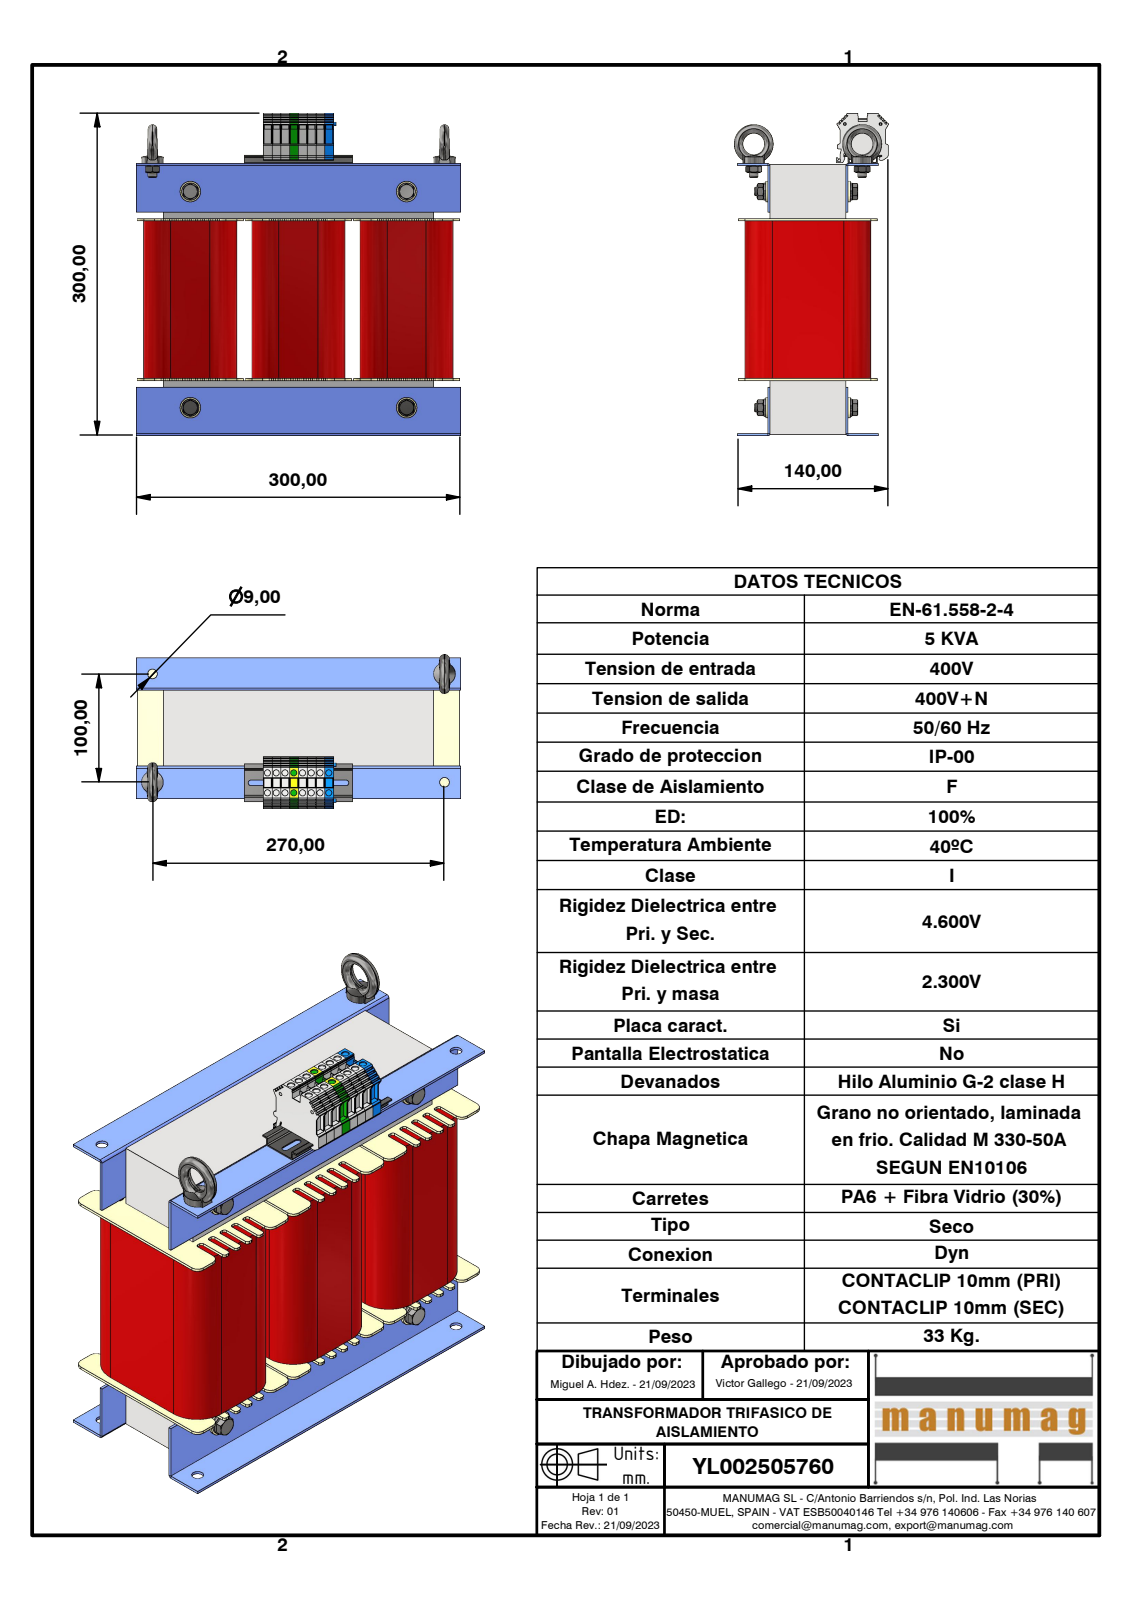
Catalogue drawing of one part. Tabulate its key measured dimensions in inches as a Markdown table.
| quantity | value |
| --- | --- |
| part name | YL002505760; 3UI150 250 x 250 - 70 (Rc50); UI 150_70; RC50 NT050 (+8 more) |
| STEP written by | Autodesk Inventor 2023 (AUTOMOTIVE_DESIGN) |
| units | inches |
| bodies | 45 solids, 3220 faces (2108 planar, 936 cylindrical, 176 other) |
| overall size | 11.811 × 11.752 × 5.607 |
| volume | 384.8 in³ |
| surface area | 1 314 in² |
| round holes (diameter × count) | 0.224 × 16, 0.262 × 6, 0.433 × 6, 0.315 × 4, 0.331 × 4, 0.354 × 4, 0.413 × 4, 0.094 × 2, 0.098 × 2, 0.108 × 2, 0.787 × 2 |
| round bosses / shafts (diameter × count) | 0.748 × 4, 0.63 × 4, 0.449 × 4, 0.378 × 4, 0.288 × 4, 1.417 × 2, 0.315 × 2, 0.276 × 2 |
| partial cylindrical surfaces (radius × count) | 0.079 × 113, 0.012 × 81, 0.236 × 24, 0.039 × 14, 0.984 × 12, 0.016 × 8, 0.102 × 8, 0.02 × 4 |
| main face-to-face distances | 1.969, 3.937, 0.079, 7.874, 2.756, 5.906, 9.843, 0.039, 2.008, 7.835 |
| hole center spacings | 0.319, 0.791, 0.638, 0.965, 0.957, 1.2, 0.724, 1.276 |
